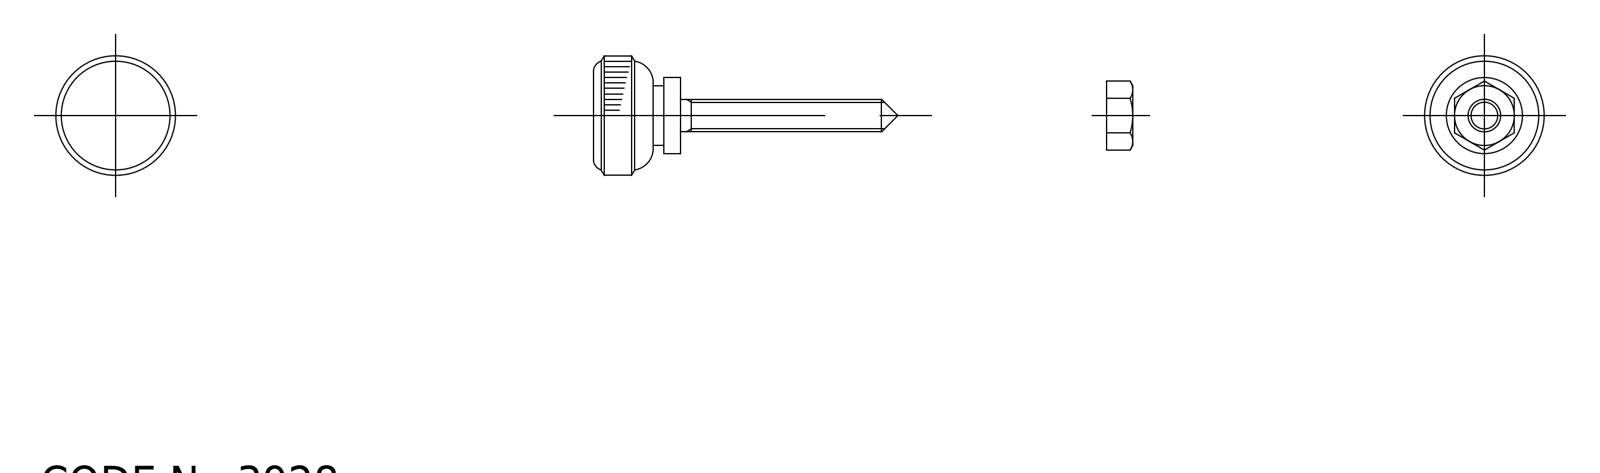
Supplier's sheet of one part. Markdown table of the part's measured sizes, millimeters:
| quantity | value |
| --- | --- |
| part name | nut; knob; THA_188_2_1474_36 |
| STEP written by | CADfix (AUTOMOTIVE_DESIGN) |
| units | millimeters |
| bodies | 2 solids, 36 faces (0 planar, 0 cylindrical, 36 other) |
| overall size | 28 × 11 × 11 |
| volume | 711 mm³ |
| surface area | 679 mm² |
